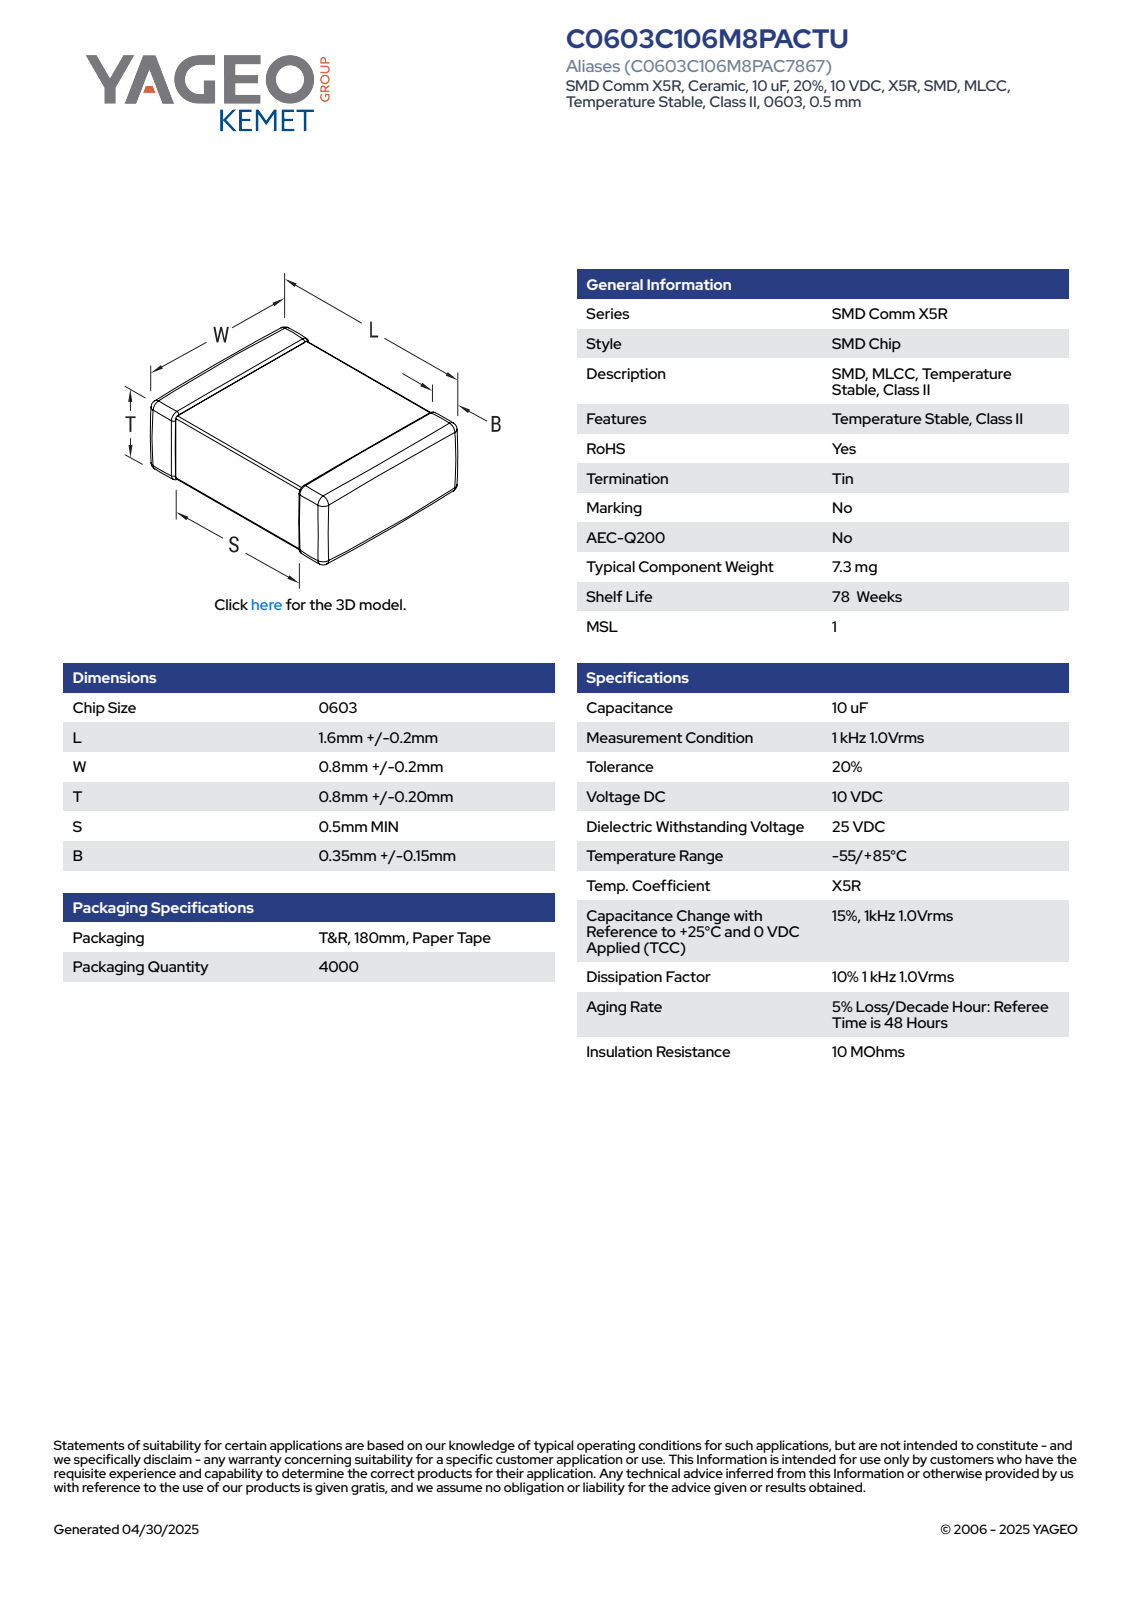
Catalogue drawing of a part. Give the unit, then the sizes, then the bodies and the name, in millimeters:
Units: millimetres
Overall size (bounding box): 1.8 × 1 × 1
Main face-to-face distances: 0.98, 0.96, 1, 1.8, 0.82, 0.97, 0.83, 0.4, 0.6, 0.41
Volume: 2 mm³ · Surface area: 9 mm²
Bodies: 4 solids, 121 faces (71 planar, 34 cylindrical, 16 other)
Part name (STEP PRODUCT): CCS_CCSTD_0603_L1.8W1T1B0.35
STEP written by: SolidWorks 2014 (AUTOMOTIVE_DESIGN)
